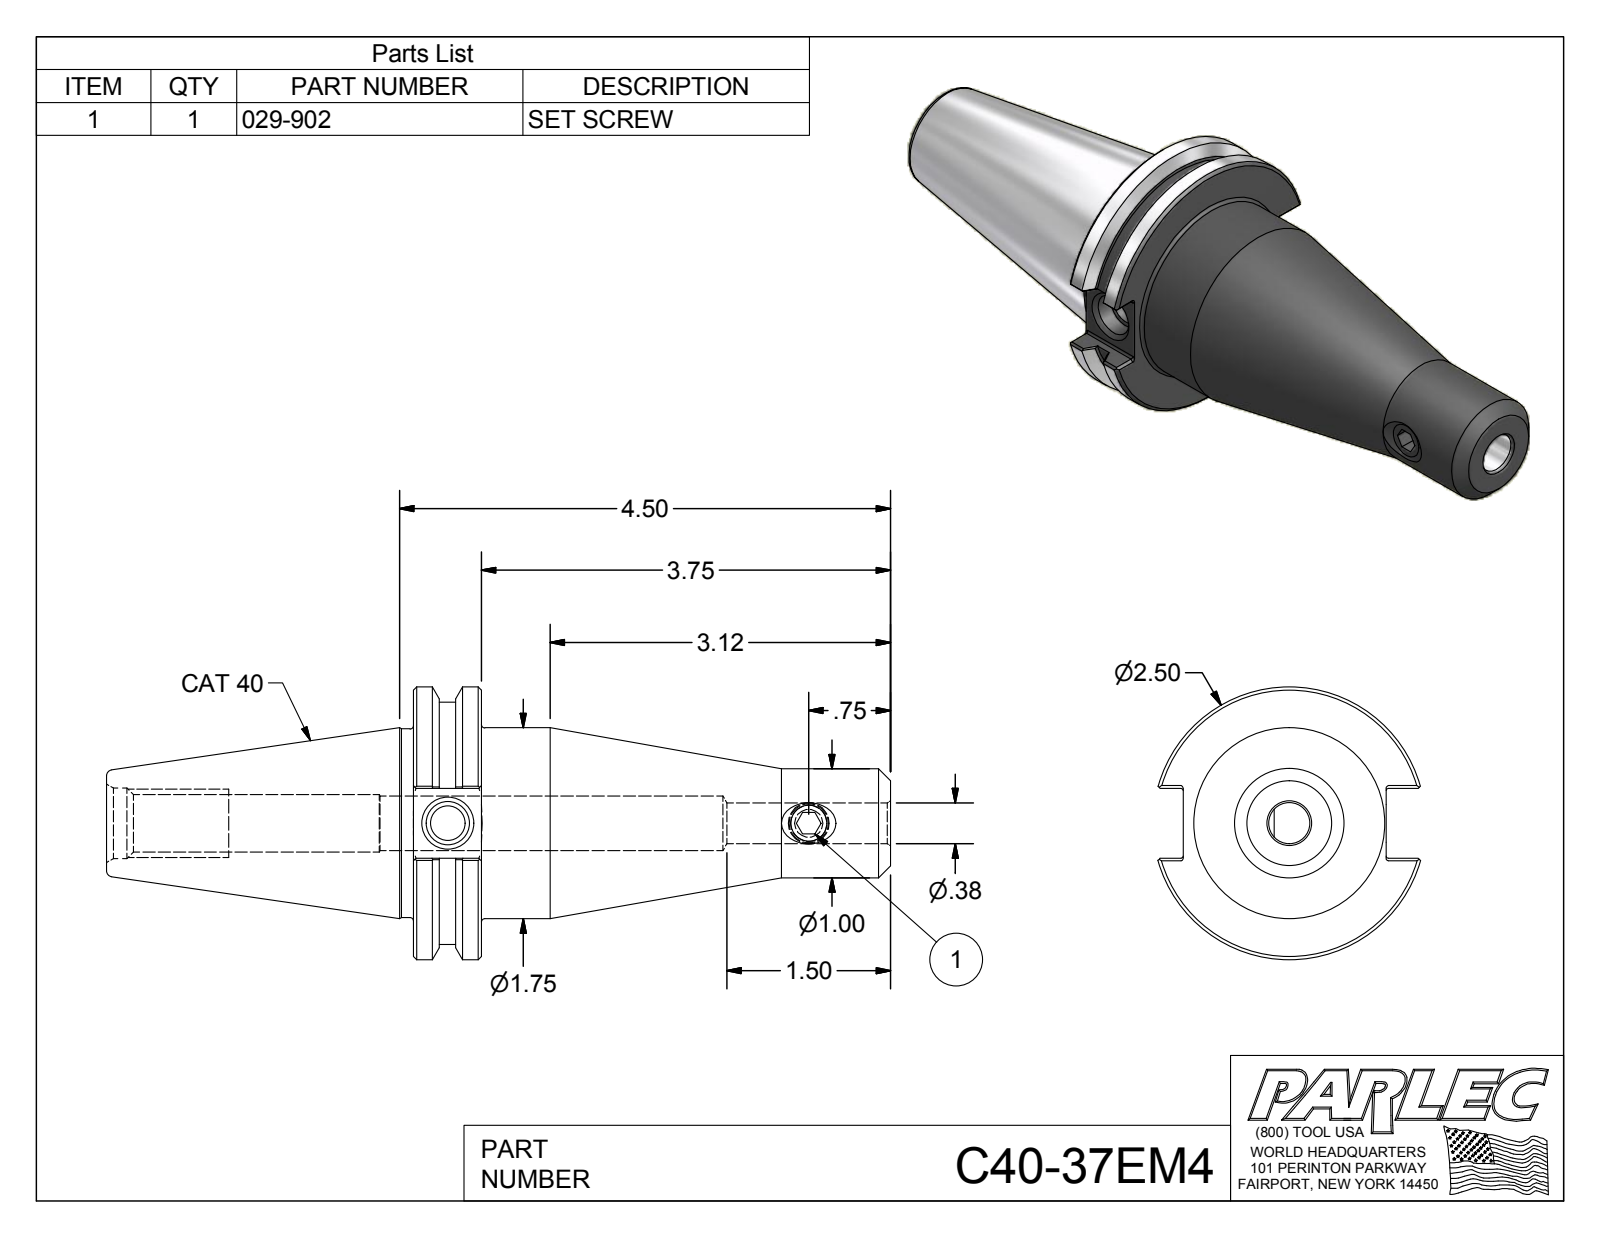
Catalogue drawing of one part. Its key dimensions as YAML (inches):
part_name: "C40-37EM4; C40-37EM4-1; 029-902"
step_written_by: "Autodesk Inventor 2012 (AUTOMOTIVE_DESIGN)"
units: inches
bodies: {solids: 2, faces: 59, planar: 19, cylindrical: 15, other: 25}
overall_size: [7.188, 2.5, 2.417]
volume: 10.91
surface_area: 51.38
round_holes:
  - {diameter: 0.33, count: 1}
  - {diameter: 0.375, count: 1}
  - {diameter: 0.527, count: 1}
  - {diameter: 0.563, count: 1}
  - {diameter: 0.648, count: 1}
round_bosses_or_shafts:
  - {diameter: 2.5, count: 1}
  - {diameter: 2.219, count: 1}
  - {diameter: 1.75, count: 1}
  - {diameter: 1, count: 1}
  - {diameter: 0.375, count: 1}
face_to_face_distances: [0.625, 4.375, 3.75, 0.64, 2.813, 3.437, 7.187, 1.871, 0.197, 1.375]
hole_center_spacings: [3.31]
